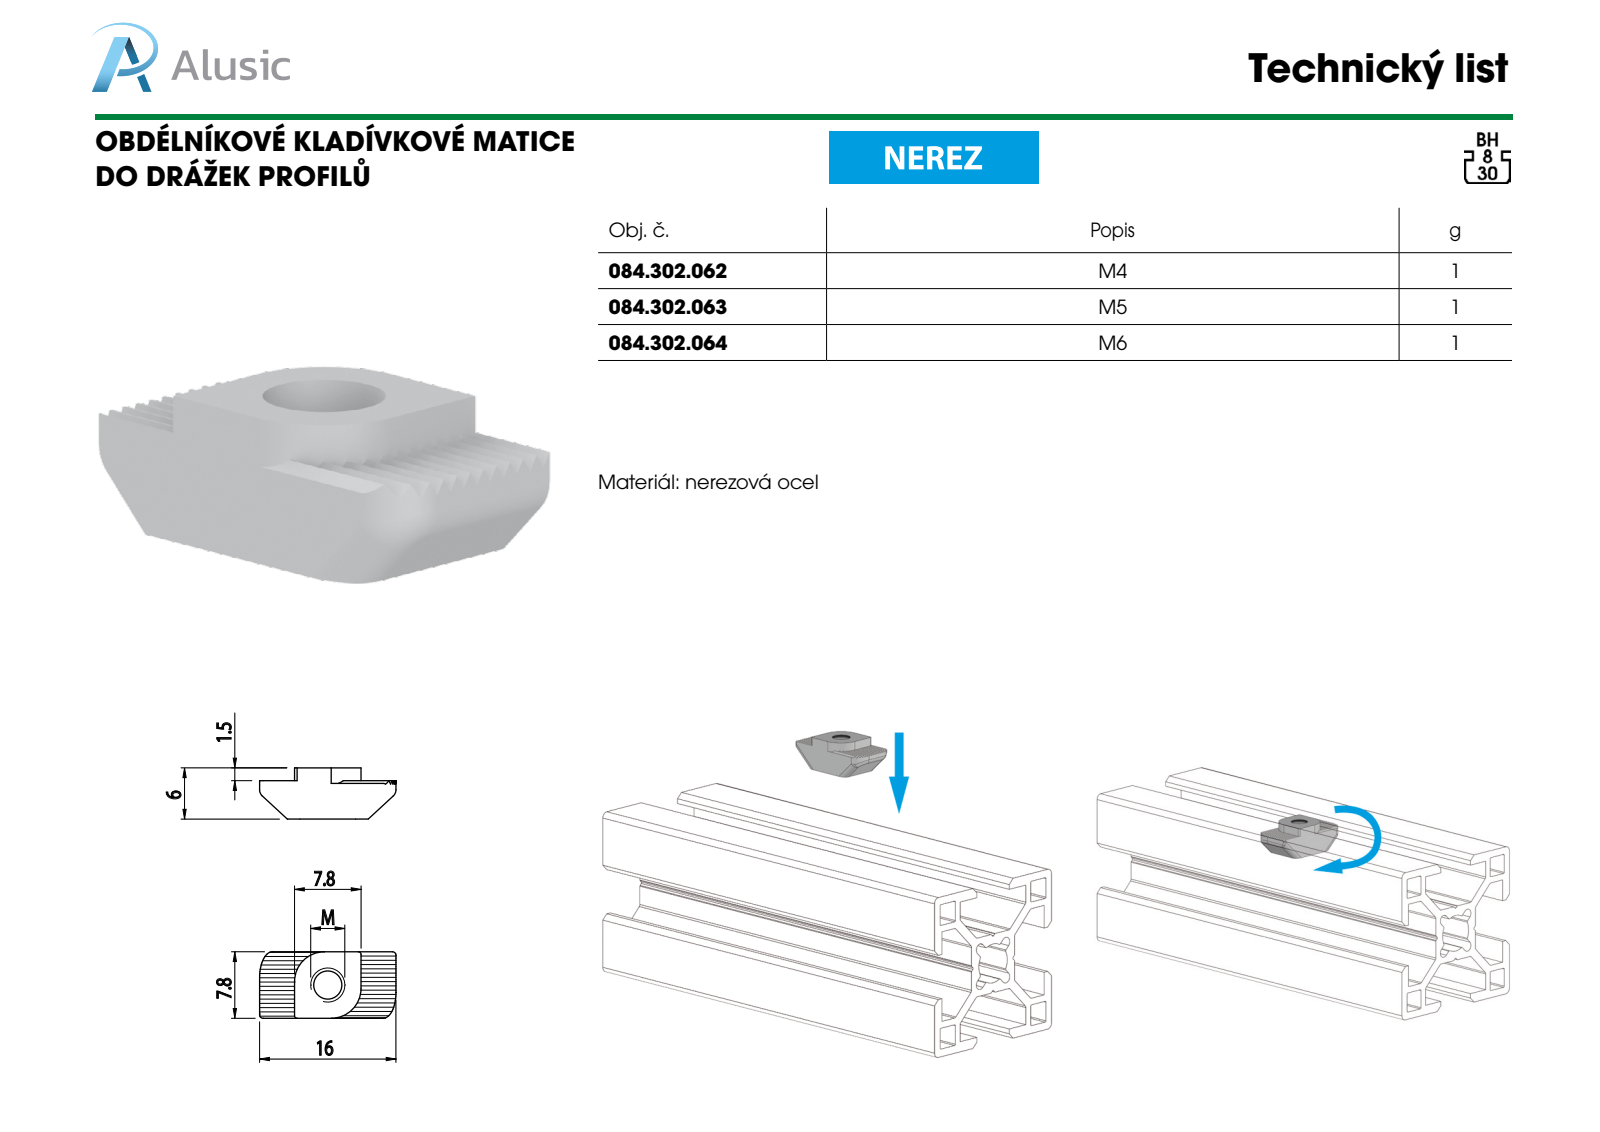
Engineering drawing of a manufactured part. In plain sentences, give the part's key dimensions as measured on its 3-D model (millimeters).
The part is named "084.302.062". Its 3-D file was written by "SolidWorks 2016 (CONFIG_CONTROL_DESIGN)". It is 1 solid with 100 faces: 76 planar, 14 cylindrical and 10 other. Overall it measures 16 by 7.8 by 6 millimeters. Its volume is 496 cubic millimeters and its surface area 544 square millimeters. Round holes: 1 of diameter 3.3. Partial cylindrical surfaces (rounded edges, fillets, slot ends): 6 of radius 1, 2 of radius 0.3, 2 of radius 0.4, 2 of radius 3.5. The main face-to-face distances are 7.8, 6, 0.85, 0.42, 1.27, 2.12, 0.43, 1.7, 4.24, 3.56.
